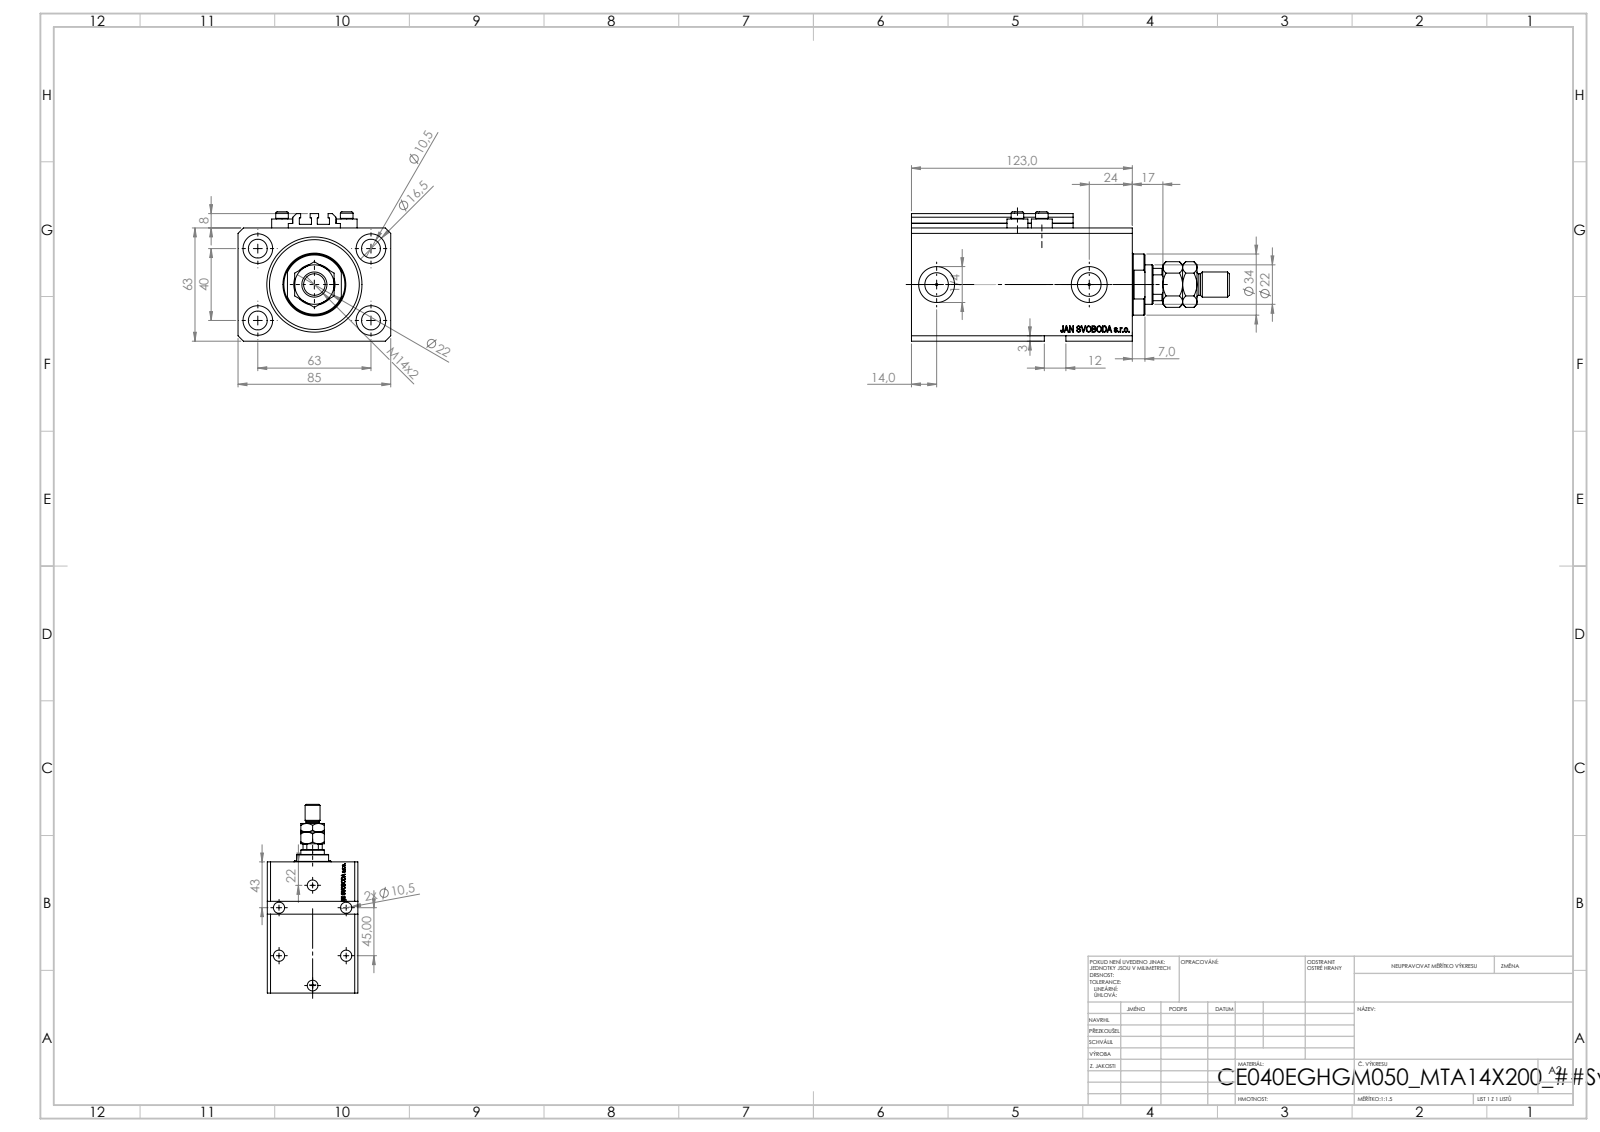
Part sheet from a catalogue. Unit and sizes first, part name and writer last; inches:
Units: inches
Overall size (bounding box): 6.969 × 3.346 × 2.835
Round holes (diameter × count): ⌀0.413 ×8, ⌀0.049 ×4, ⌀0.157 ×4, ⌀0.65 ×4, ⌀0.394 ×2, ⌀0.518 ×2, ⌀0.787 ×2, ⌀0.492 ×1, ⌀0.866 ×1, ⌀1.575 ×1, ⌀2.087 ×1
Round bosses / shafts (diameter × count): ⌀0.457 ×4, ⌀0.276 ×4, ⌀1.339 ×1, ⌀0.551 ×1, ⌀0.472 ×1
Partial cylindrical surfaces — rounded edges, fillets, slot ends (radius × count): R0.008 ×10, R0.413 ×1
Main face-to-face distances: 2.48, 3.346, 0.669, 4.843, 4.173, 0.449, 3.724, 4.394, 0.118, 2.559
Hole centre spacings: 1.469, 2.48, 0.535, 0.606, 0.983, 1.084, 1.324, 1.417
Volume: 34.61 in³ · Surface area: 189.7 in²
Bodies: 9 solids, 1156 faces (550 planar, 150 cylindrical, 456 other)
Part name (STEP PRODUCT): ALLEN BOLT V250CE; V250CE_C_VCP; V250CE_E_Body; V250CE_VC_E (+1 more)
STEP written by: SolidWorks 2019 (CONFIG_CONTROL_DESIGN)
